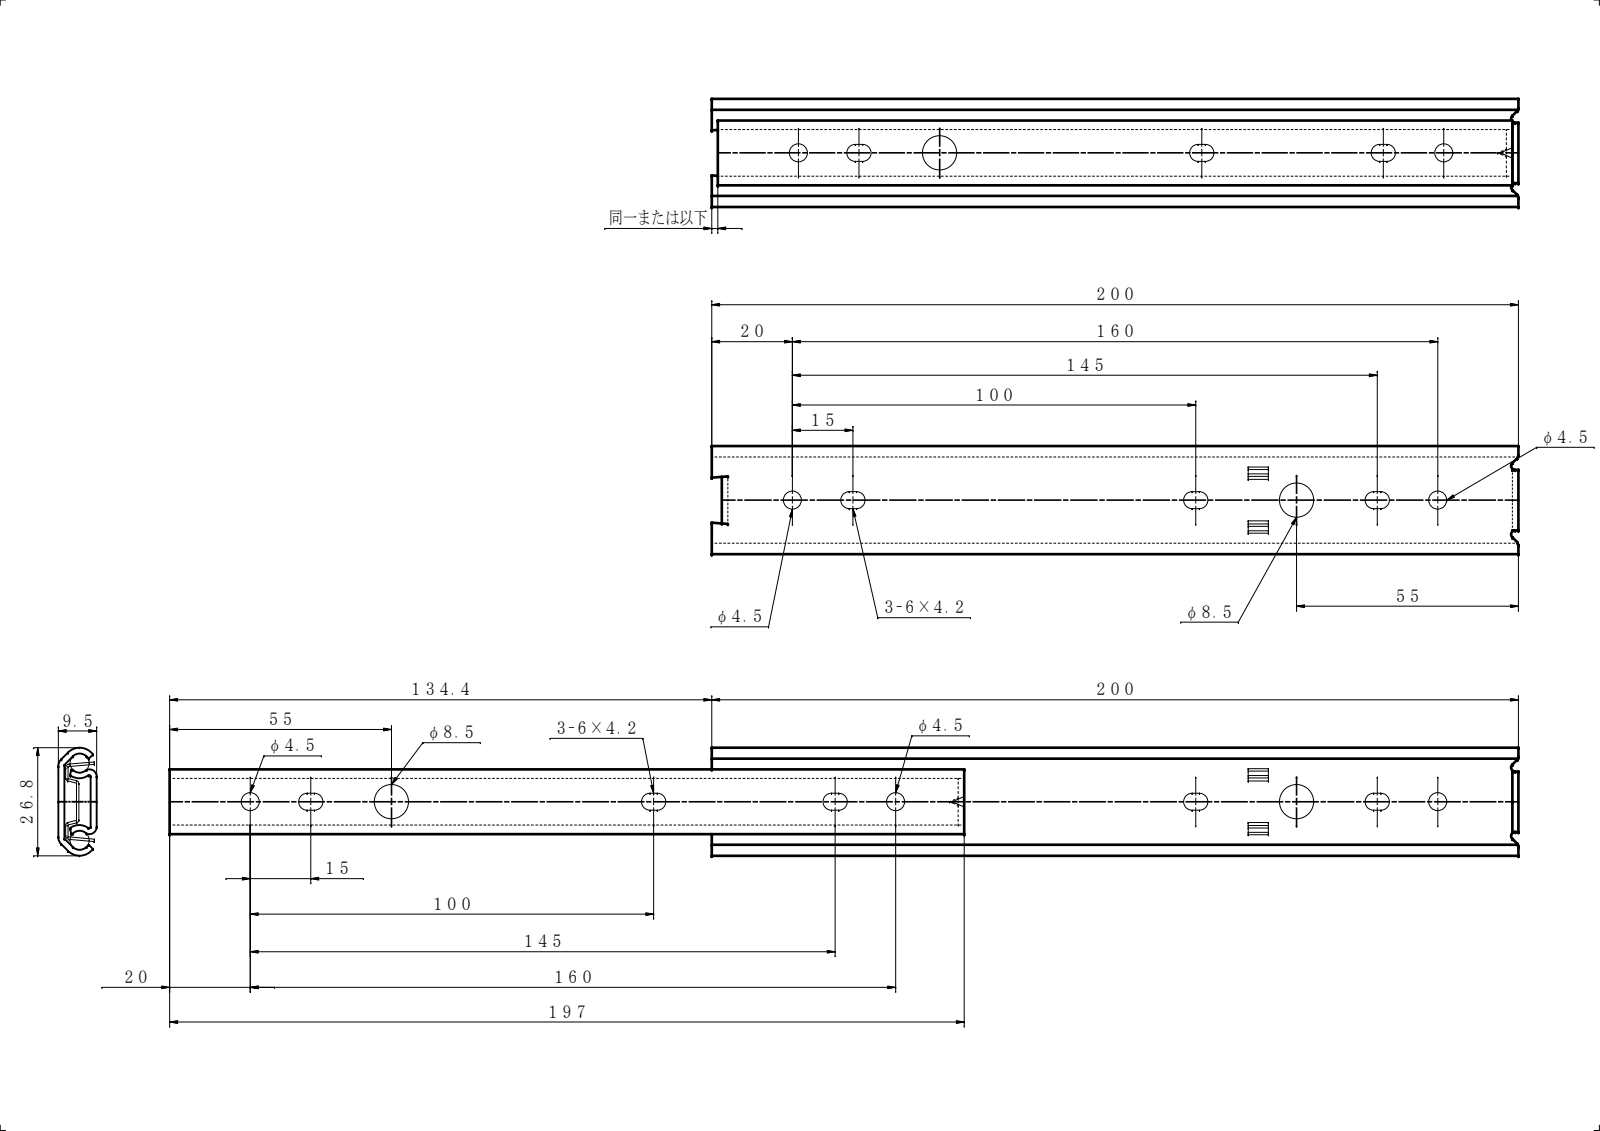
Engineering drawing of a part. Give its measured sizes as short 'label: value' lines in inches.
name: U2721-200 OM; U2721-200 IM; U2721_200
written by: SolidWorks 2019 (CONFIG_CONTROL_DESIGN)
unit: in
bodies: 2 solids, 124 faces (57 planar, 67 cylindrical, 0 other)
size: 13.165 × 1.055 × 0.374
volume: 1.112 in³; area: 40.55 in²
holes: 4× ⌀0.177, 2× ⌀0.335
rounds: 12× R0.083, 10× R0.079, 5× R0.039, 4× R0.02, 2× R0.007, 2× R0.051, 2× R0.066, 2× R0.094
face distances: 0.059, 0.315, 0.374, 0.256, 5.409, 5.35, 7.717, 2.308, 5.469, 7.776
hole spacings: 1.378, 3.913, 4.921, 5.291, 6.299, 10.213, 1.008, 8.835
